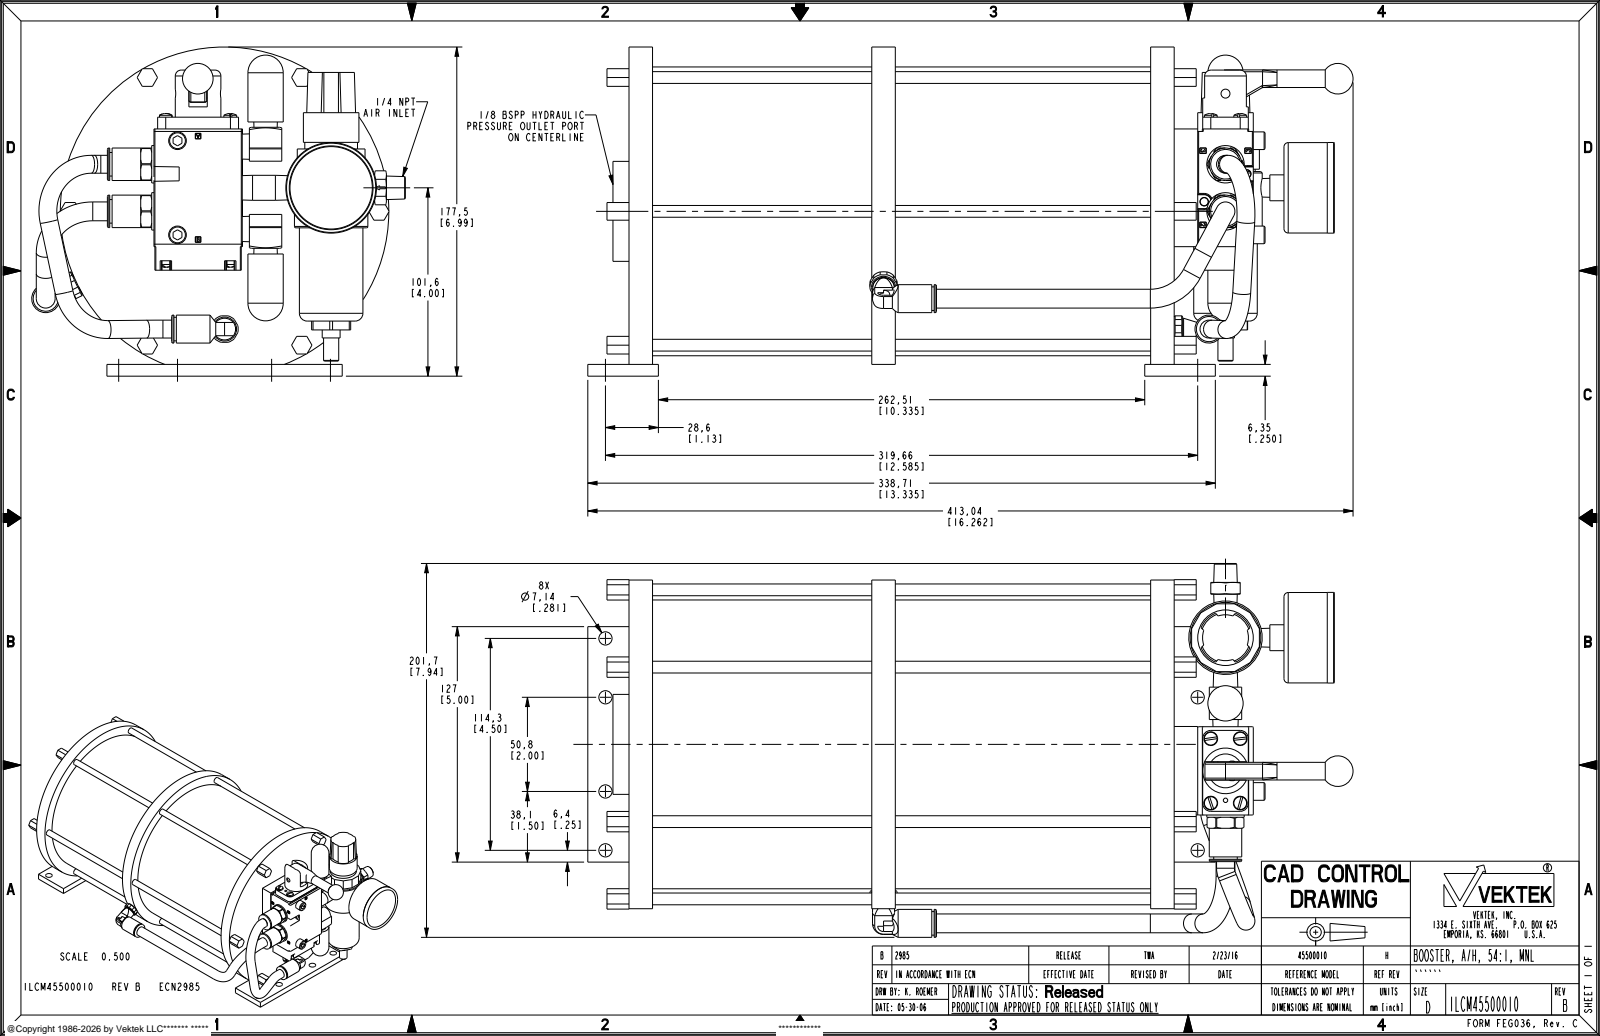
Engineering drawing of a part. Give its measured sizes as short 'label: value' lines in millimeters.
name: ILCM45500010
written by: PRO/ENGINEER BY PARAMETRIC TECHNOLOGY CORPORATION, 2013320 (CONFIG_CONTROL_DESIGN)
unit: mm
bodies: 1 solid, 1189 faces (552 planar, 330 cylindrical, 307 other)
size: 413.04 × 201.66 × 177.55
volume: 5 982 000 mm³; area: 376 619 mm²
holes: 12× ⌀7.14, 4× ⌀5.11, 3× ⌀12.7, 2× ⌀5.41, 2× ⌀6.65, 2× ⌀13.72, 2× ⌀17.53, 2× ⌀20.17, 1× ⌀2.38, 1× ⌀2.5, 1× ⌀3.68, 1× ⌀4.83
bosses: 12× ⌀6.35, 6× ⌀9.65, 4× ⌀10.16, 4× ⌀9.53, 4× ⌀6.9, 3× ⌀11.68, 2× ⌀15.09, 2× ⌀12.7
rounds: 19× R1, 16× R0.5, 6× R1.52, 4× R0.51, 4× R3.3, 4× R3.7, 4× R4.37, 4× R5.96
face distances: 294.26, 12.7, 281.56, 131.04, 150.52, 6.35, 163.22, 143.74, 118.34, 268.86
hole spacings: 50.8, 19.05, 31.75, 37.03, 54.25, 82.55, 84.72, 300.61
